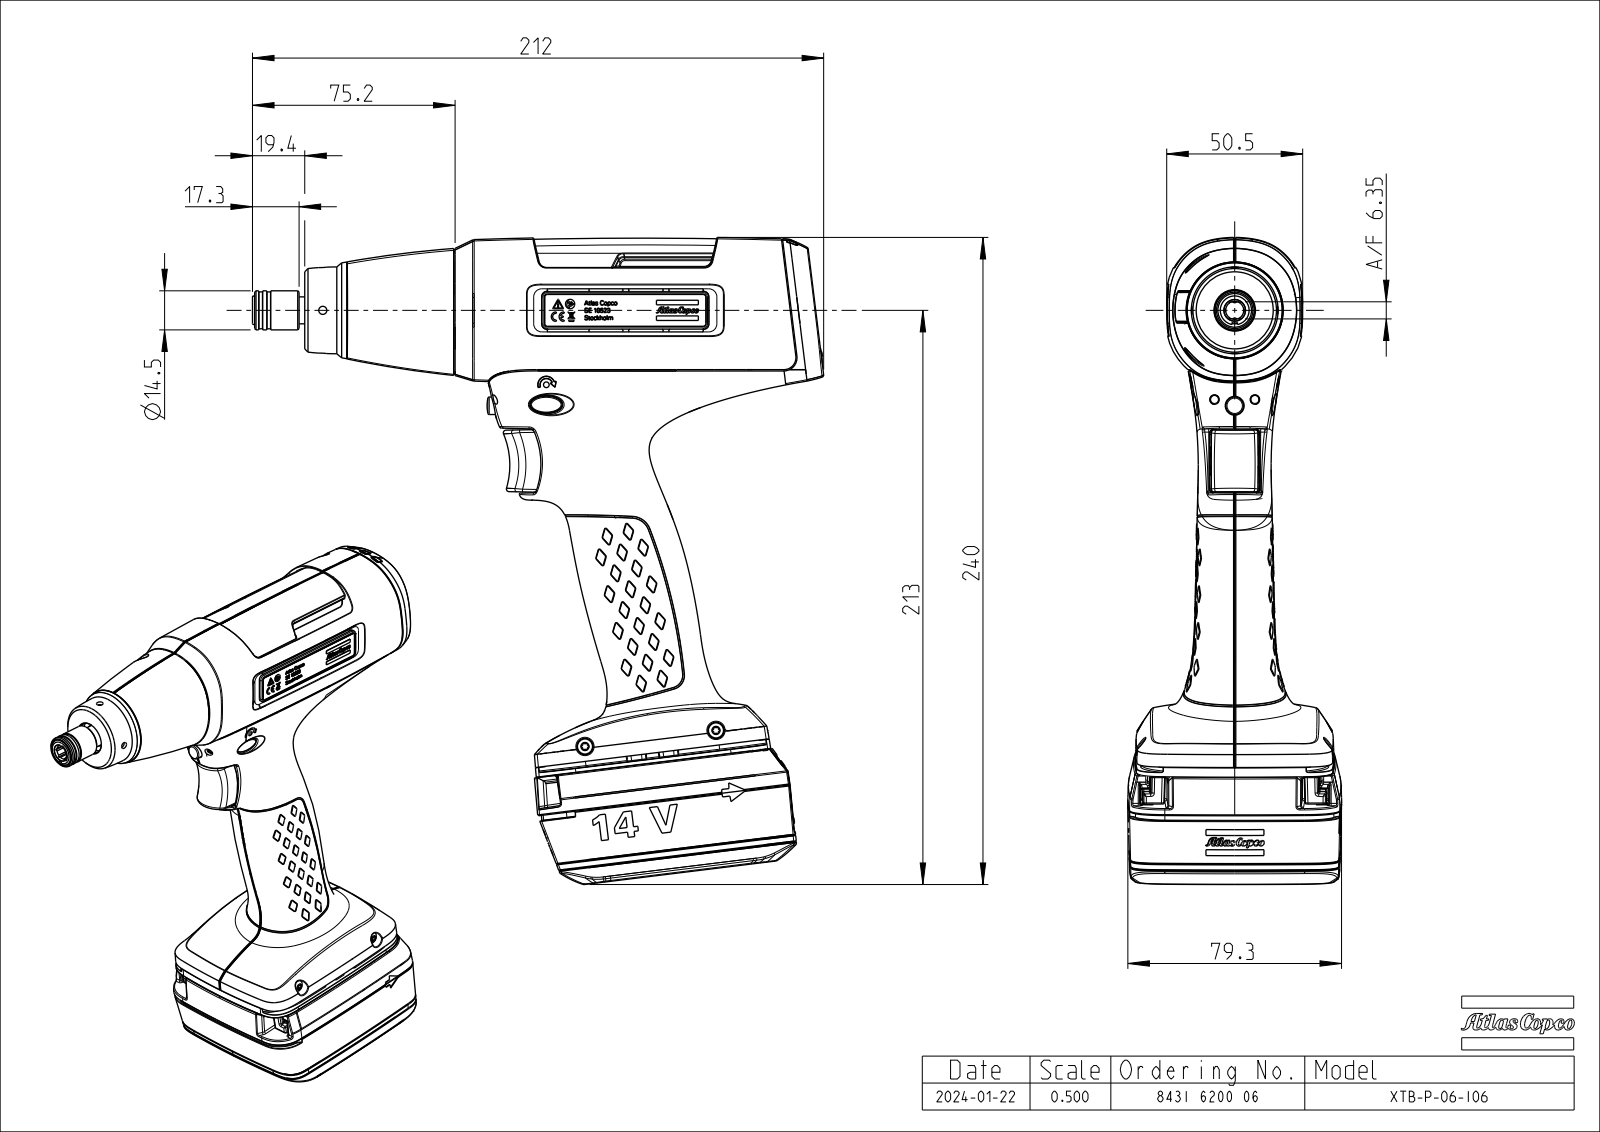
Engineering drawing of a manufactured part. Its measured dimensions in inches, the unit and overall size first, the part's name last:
Units: inches
Overall size (bounding box): 8.348 × 8.277 × 2.907
Round holes (diameter × count): ⌀0.13 ×4, ⌀0.118 ×3, ⌀0.043 ×2, ⌀0.11 ×2, ⌀0.091 ×1, ⌀0.22 ×1, ⌀0.264 ×1, ⌀0.295 ×1, ⌀0.417 ×1, ⌀0.48 ×1, ⌀0.492 ×1, ⌀0.591 ×1
Round bosses / shafts (diameter × count): ⌀0.571 ×1, ⌀0.539 ×1, ⌀0.394 ×1, ⌀0.362 ×1, ⌀0.346 ×1, ⌀0.213 ×1, ⌀0.134 ×1
Partial cylindrical surfaces — rounded edges, fillets, slot ends (radius × count): R0.008 ×197, R0.004 ×144, R0.02 ×116, R0.039 ×93, R0.012 ×41, R0.011 ×12, R0.02 ×12, R0.031 ×10
Main face-to-face distances: 0.531, 0.12, 1.063, 0.031, 0.118, 0.016, 0.413, 0.039, 0.013, 0.102
Hole centre spacings: 1.575, 2.323, 2.806, 0.268, 0.526, 0.907, 1.157, 7.435
Volume: 37.82 in³ · Surface area: 144 in²
Bodies: 2 solids, 5831 faces (2522 planar, 1094 cylindrical, 2215 other)
Part name (STEP PRODUCT): RAJAT_XB
STEP written by: CREO PARAMETRIC BY PTC INC, 2022414 (CONFIG_CONTROL_DESIGN)
